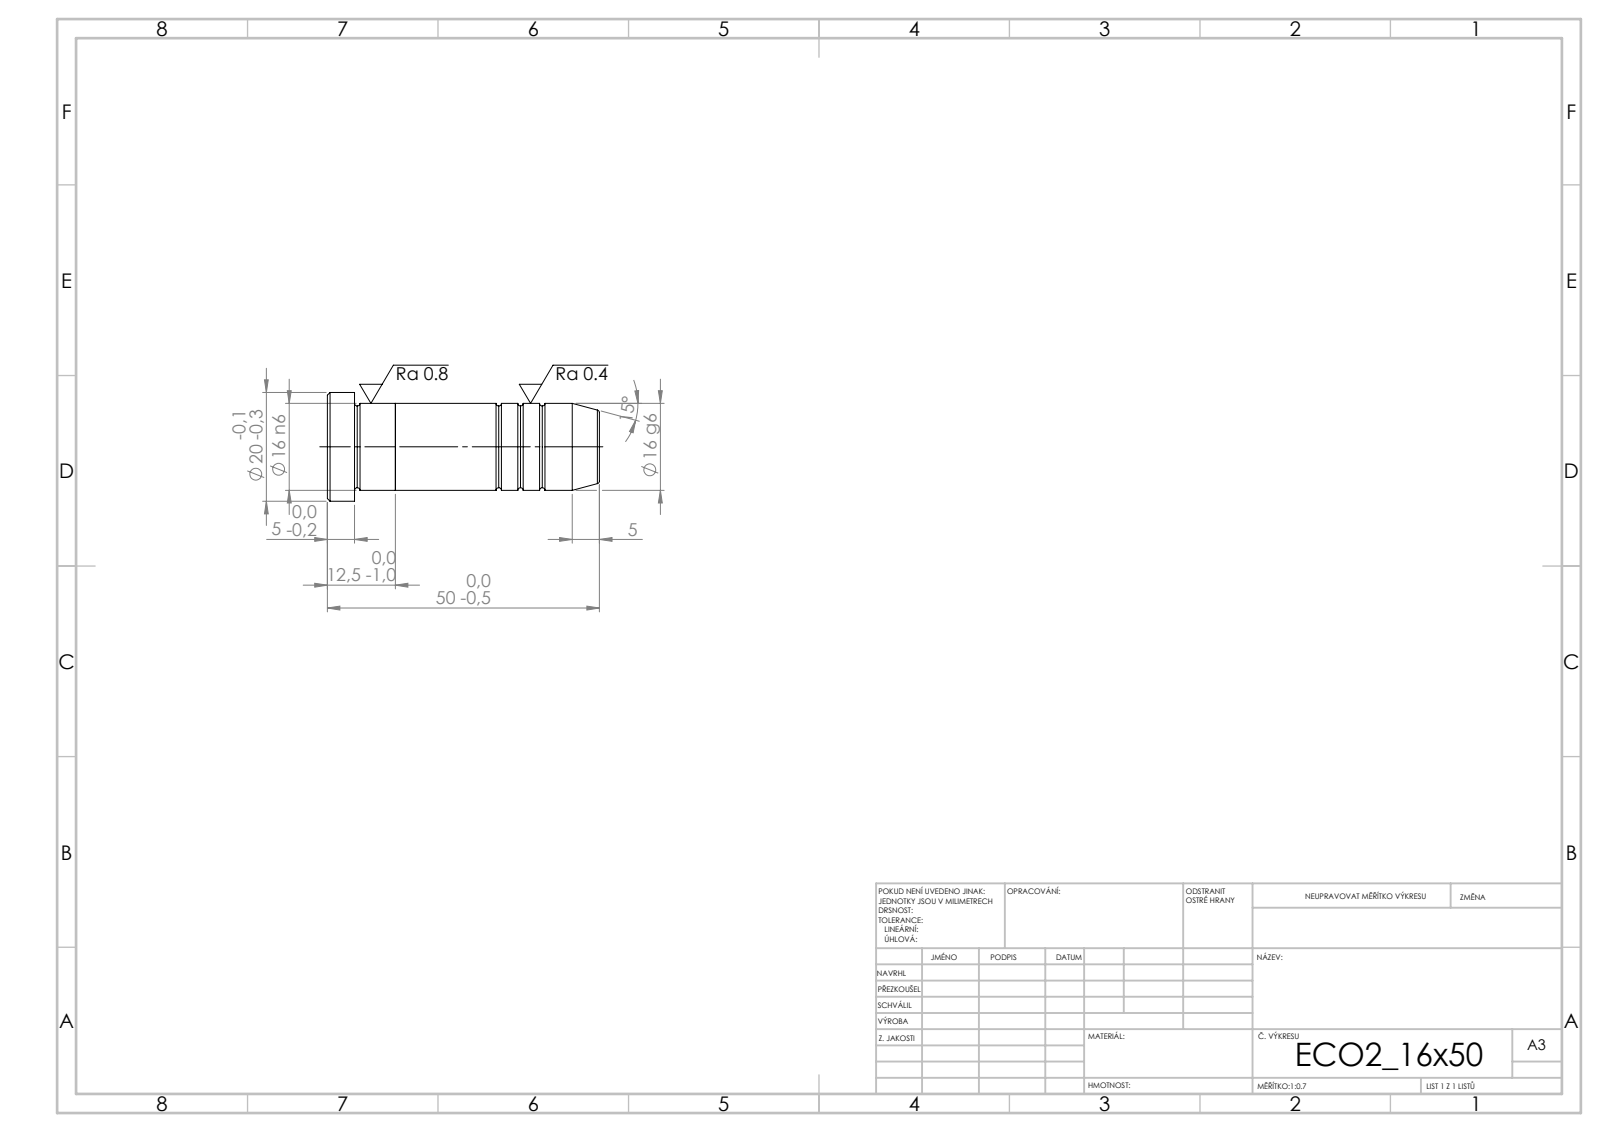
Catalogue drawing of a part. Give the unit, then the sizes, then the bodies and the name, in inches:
Units: inches
Overall size (bounding box): 1.969 × 0.787 × 0.787
Round bosses / shafts (diameter × count): ⌀0.787 ×1, ⌀0.63 ×1
Main face-to-face distances: 0.492, 1.476, 1.969, 1.772, 0.295, 0.197
Volume: 0.633 in³ · Surface area: 5.597 in²
Bodies: 2 solids, 39 faces (5 planar, 12 cylindrical, 22 other)
STEP written by: SolidWorks 2019 (CONFIG_CONTROL_DESIGN)
